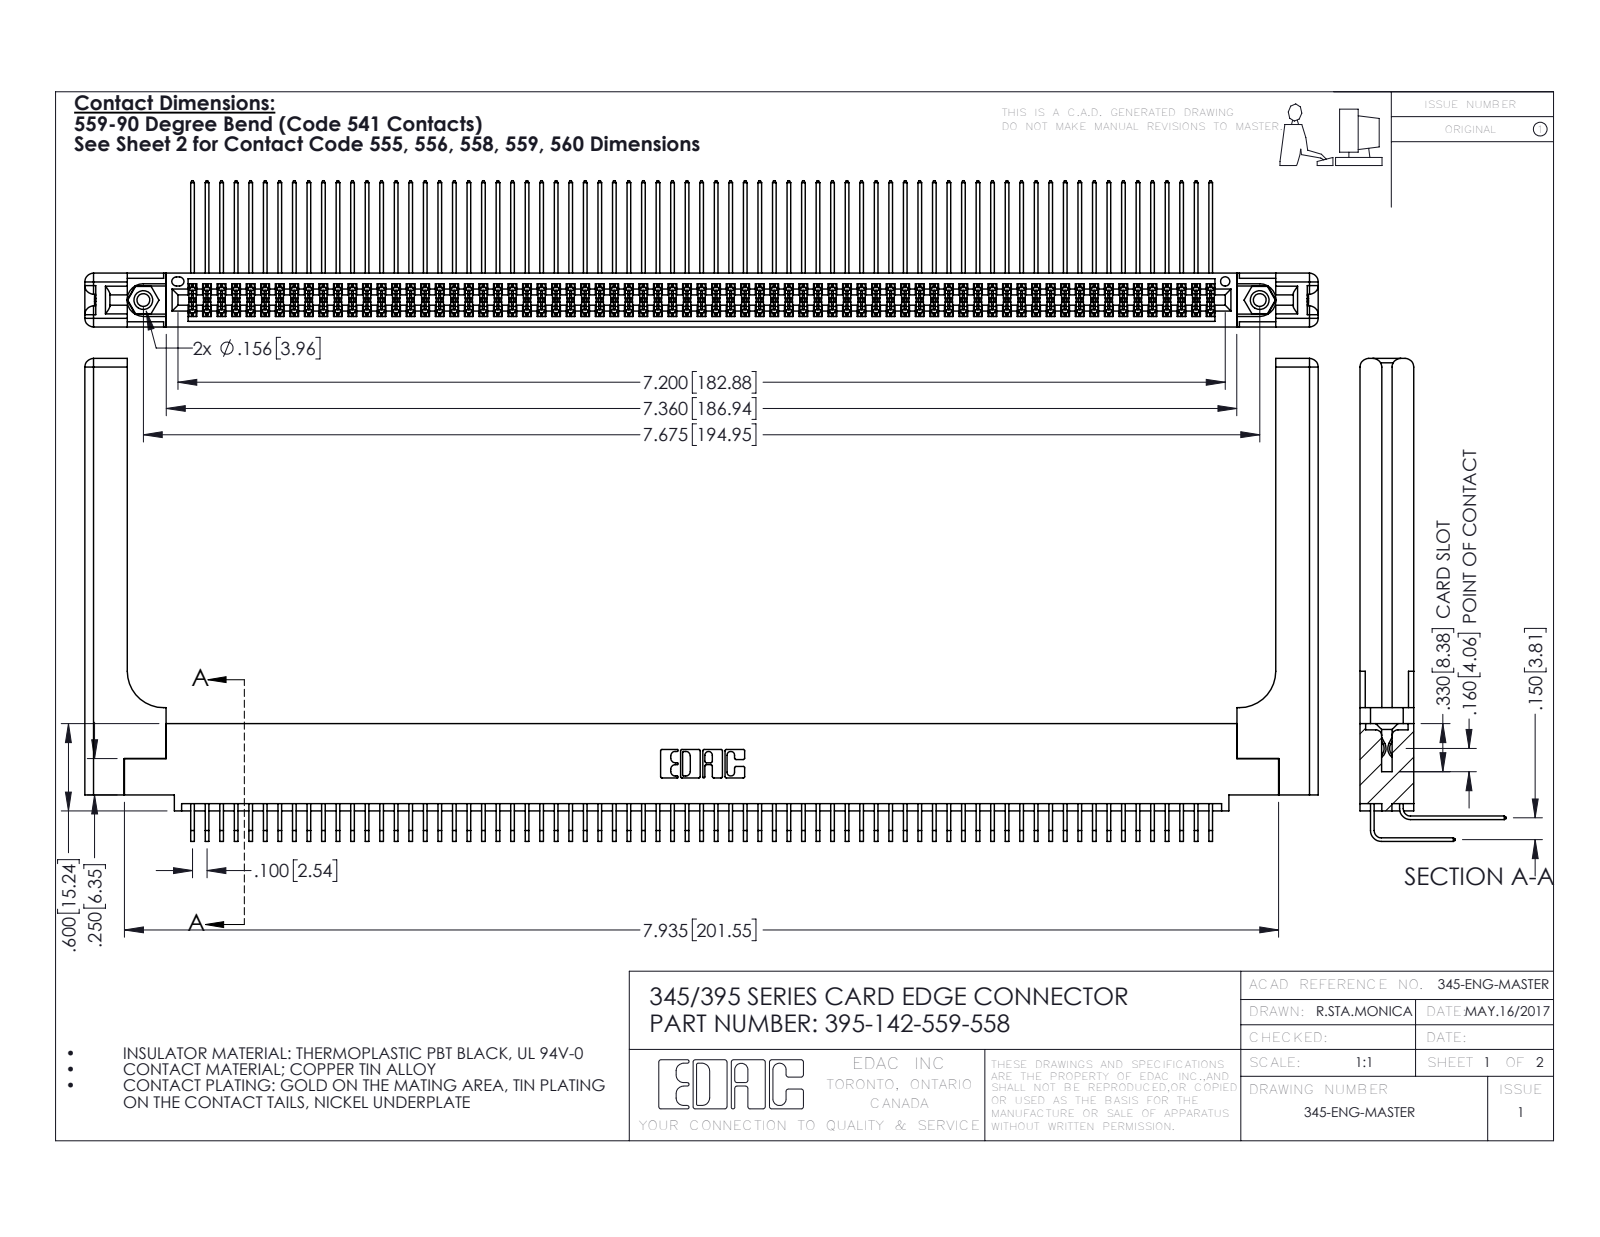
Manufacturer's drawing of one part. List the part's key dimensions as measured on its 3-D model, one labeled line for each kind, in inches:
Part name (STEP PRODUCT): 345 Part_0.110 Offset - 0.156 Dia-TH; 345-292-001_558 559 Tail - 1; 345-292-001_559 Tail - 2; 345-220-058_345-220-058 (+2 more)
STEP written by: SolidWorks 2016 (CONFIG_CONTROL_DESIGN)
Units: inches
Bodies: 147 solids, 7770 faces (5202 planar, 2508 cylindrical, 60 other)
Overall size (bounding box): 8.479 × 3.319 × 1.005
Volume: 1.856 in³ · Surface area: 65.09 in²
Round holes (diameter × count): ⌀0.089 ×2, ⌀0.125 ×2, ⌀0.156 ×2, ⌀0.064 ×1
Round bosses / shafts (diameter × count): ⌀0.155 ×2
Partial cylindrical surfaces — rounded edges, fillets, slot ends (radius × count): R0.006 ×284, R0.01 ×22, R0.06 ×16, R0.007 ×6, R0.031 ×6, R0.026 ×3, R0.014 ×2, R0.019 ×2
Main face-to-face distances: 0.072, 0.298, 0.37, 0.098, 0.272, 0.025, 0.2, 0.225, 0.175, 0.15
Hole centre spacings: 0.27, 7.439, 7.675
